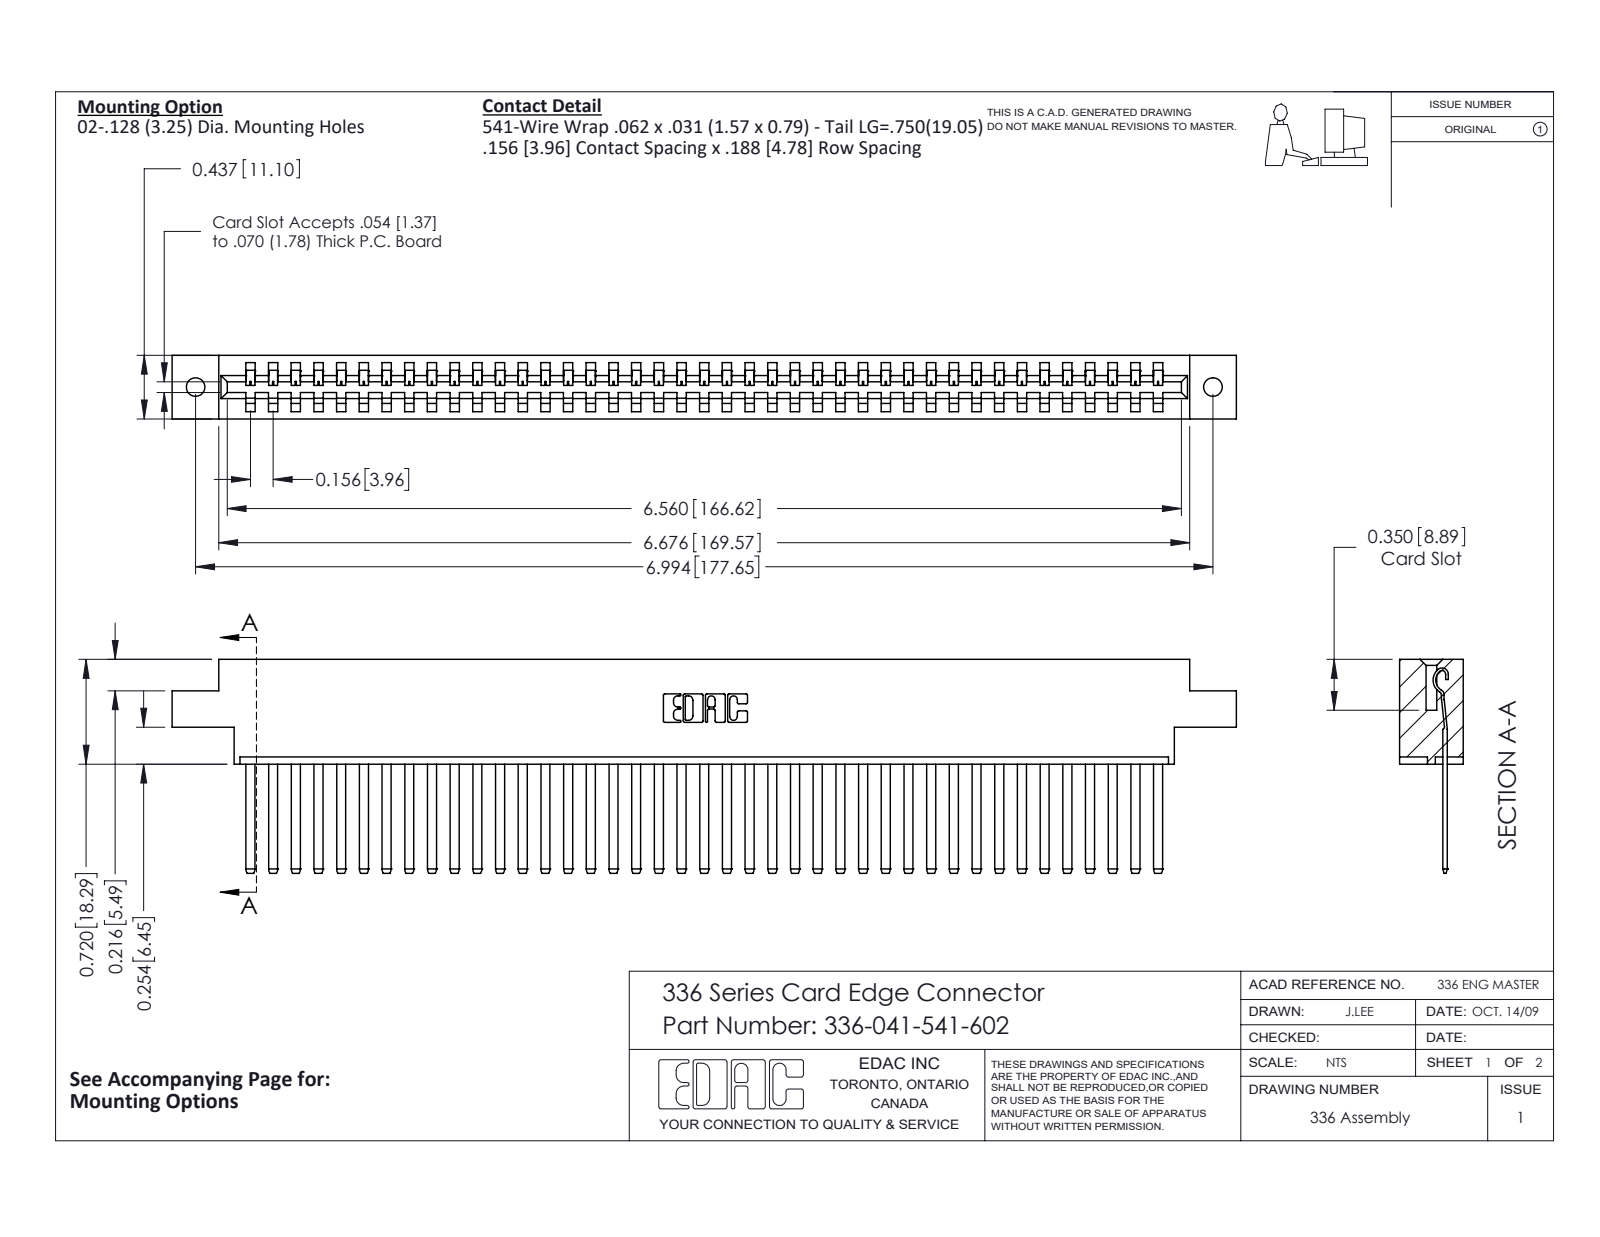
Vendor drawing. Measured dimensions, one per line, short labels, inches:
name: 336-290-001_336-290-541; 336-041-541-602; 336 Part_Offset - .128 Dia
written by: SolidWorks 2020 (CONFIG_CONTROL_DESIGN)
unit: in
bodies: 42 solids, 2168 faces (1468 planar, 700 cylindrical, 0 other)
size: 7.317 × 1.47 × 0.437
volume: 1.64 in³; area: 45.18 in²
holes: 2× ⌀0.128
rounds: 82× R0.004, 82× R0.056, 22× R0.01, 6× R0.007, 6× R0.031, 3× R0.026, 2× R0.022, 2× R0.04
face distances: 0.437, 0.181, 0.328, 0.14, 0.297, 0.109, 0.031, 0.256, 0.05, 0.387
hole spacings: 6.994
